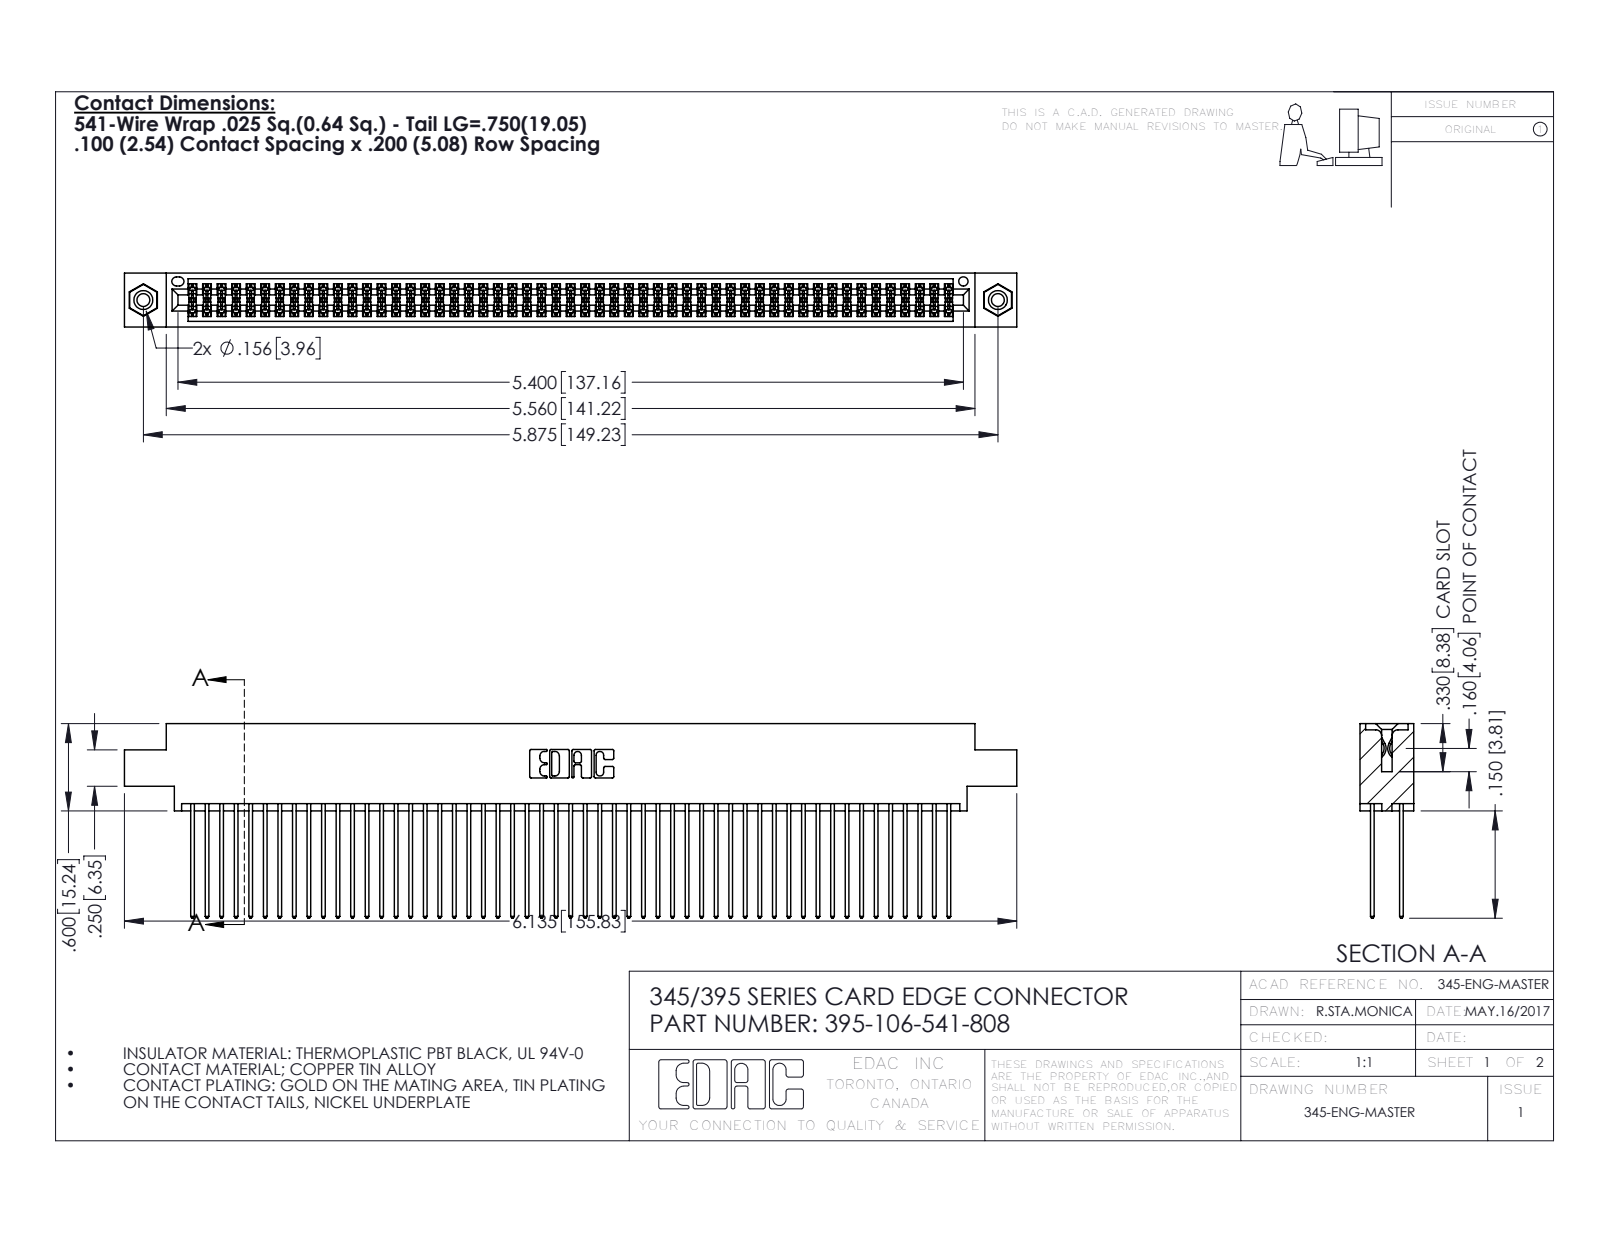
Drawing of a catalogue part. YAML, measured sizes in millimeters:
part_name: "345-292-001_345-293-141; 345-250-001_345-250-003-102; 395-106-541-808; 345 Part_0.170 Offset - 0.156 Dia-TI"
step_written_by: "SolidWorks 2016 (CONFIG_CONTROL_DESIGN)"
units: millimeters
bodies: {solids: 109, faces: 5490, planar: 3614, cylindrical: 1860, other: 16}
overall_size: [155.8, 34, 9.4]
volume: 15700
surface_area: 26480
round_holes:
  - {diameter: 2.3, count: 2}
  - {diameter: 3.2, count: 2}
  - {diameter: 4, count: 2}
  - {diameter: 1.6, count: 1}
round_bosses_or_shafts:
  - {diameter: 3.9, count: 2}
partial_cylinders:
  - {radius: 0.2, count: 159}
  - {radius: 0.3, count: 106}
  - {radius: 0.3, count: 22}
  - {radius: 0.2, count: 6}
  - {radius: 0.8, count: 6}
  - {radius: 0.7, count: 3}
  - {radius: 0.4, count: 2}
  - {radius: 0.5, count: 2}
face_to_face_distances: [1.8, 7.6, 5.1, 2.5, 6.9, 0.6, 5.7, 9.4, 4.4, 3.8]
hole_center_spacings: [6.9, 143.2, 149.2]
